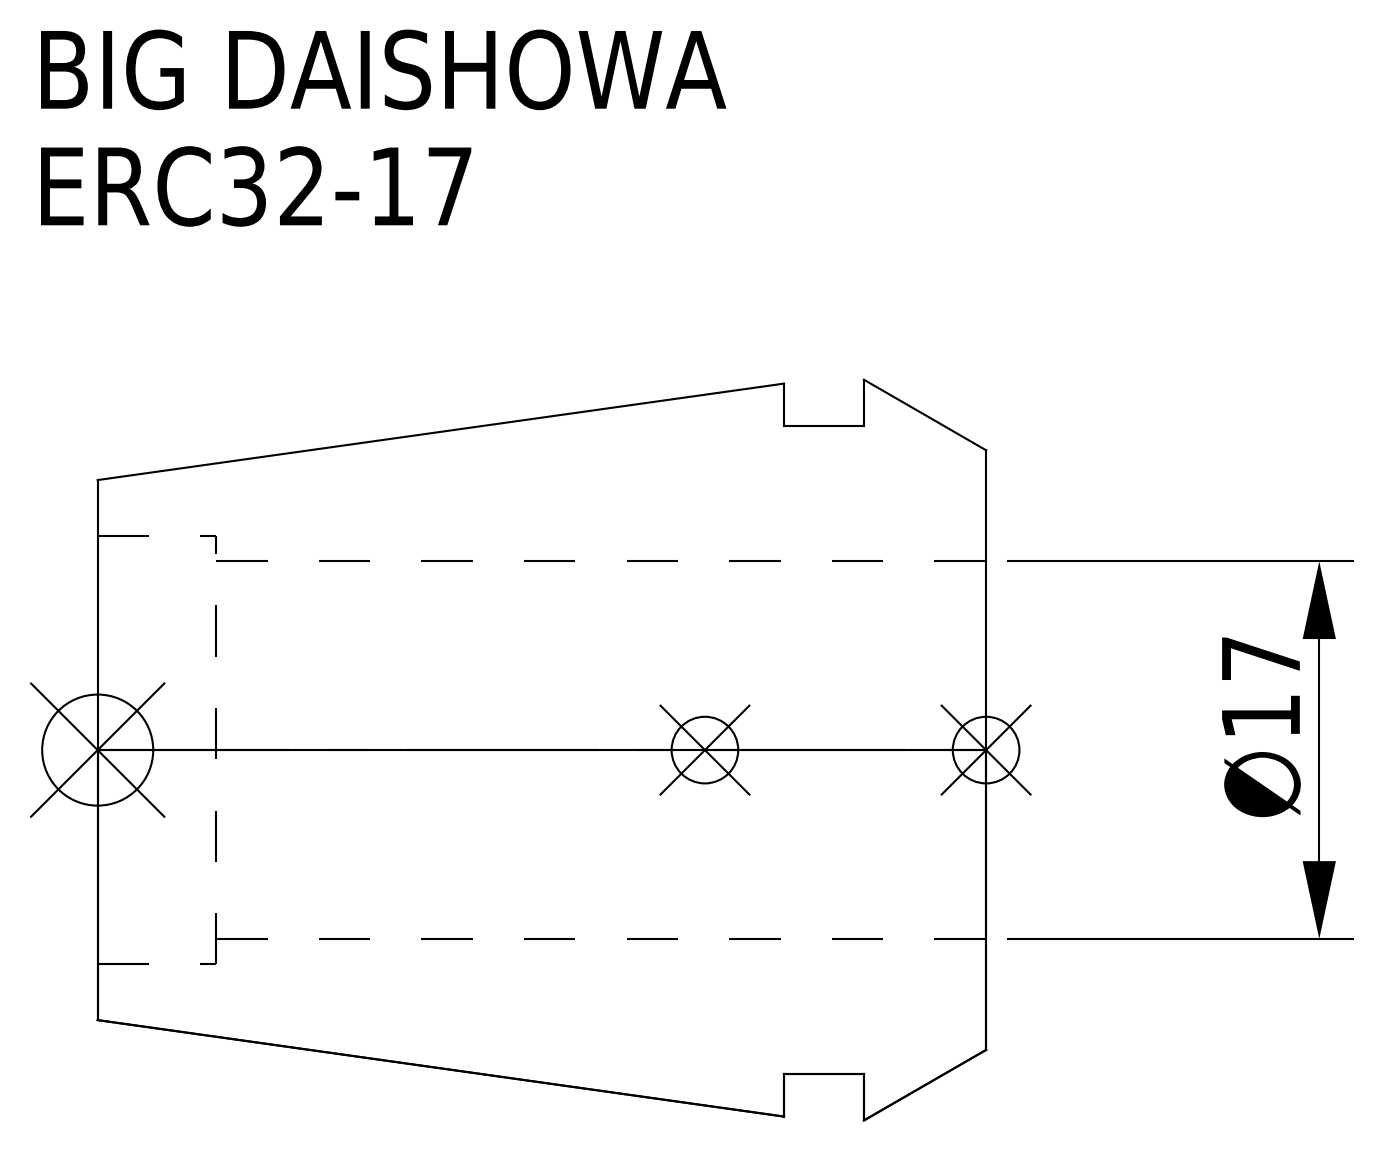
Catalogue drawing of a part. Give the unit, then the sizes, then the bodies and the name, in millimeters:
Units: millimetres
Overall size (bounding box): 40 × 33.35 × 33.35
Round holes (diameter × count): ⌀17 ×1, ⌀19.3 ×1
Round bosses / shafts (diameter × count): ⌀29.2 ×1
Main face-to-face distances: 5.5, 9.1, 3.6, 40, 34.5, 30.9, 34.67, 29.17, 25.57, 5.33
Volume: 17 013 mm³ · Surface area: 6 889 mm²
Bodies: 1 solid, 15 faces (5 planar, 6 cylindrical, 4 other)
Part name (STEP PRODUCT): ERC32-17
STEP written by: CREO PARAMETRIC BY PTC INC, 2016380 (AUTOMOTIVE_DESIGN)
